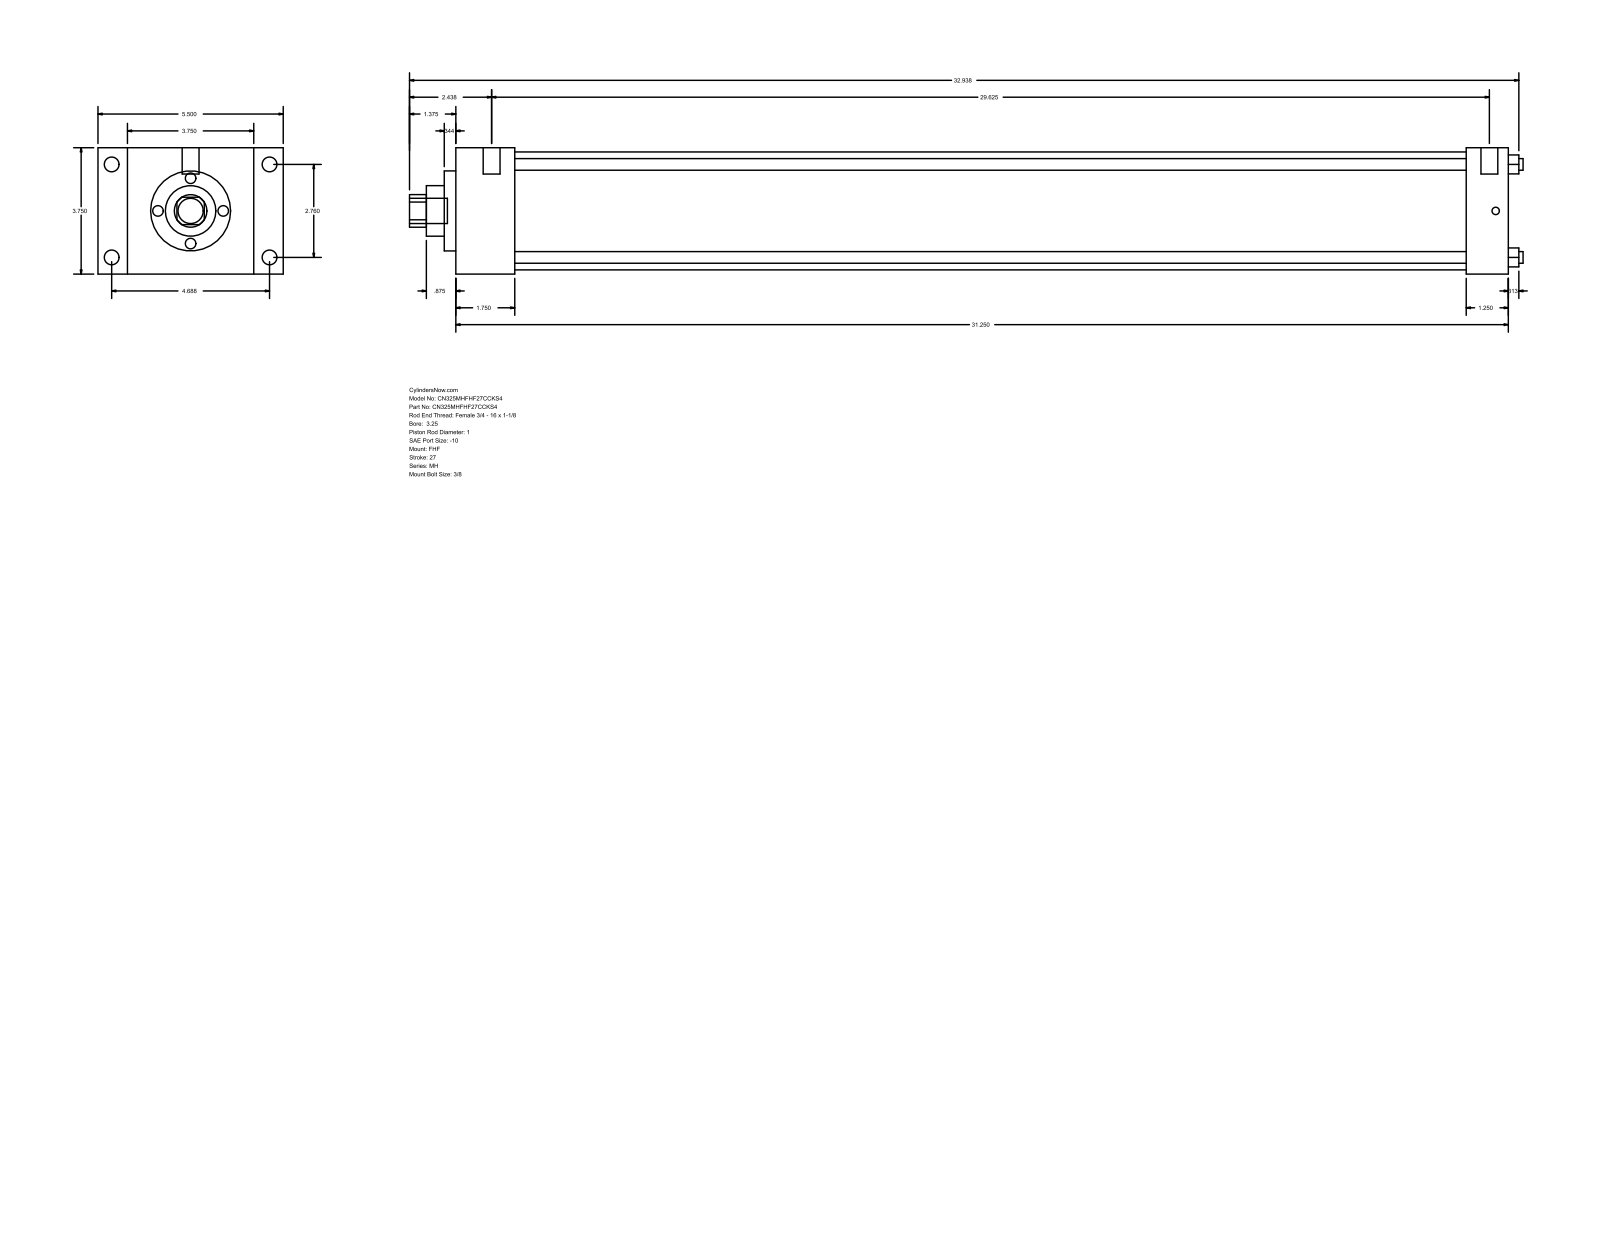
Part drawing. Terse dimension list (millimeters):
name: MH_FHF__0325_1
written by: GSSL Pune (CONFIG_CONTROL_DESIGN)
unit: mm
bodies: 0 solids, 90 faces (61 planar, 29 cylindrical, 0 other)
size: 839.79 × 139.7 × 95.25
holes: 4× ⌀8.76, 1× ⌀25.4, 1× ⌀38.1, 1× ⌀60.33, 1× ⌀88.9
bosses: 4× ⌀11.13, 4× ⌀5.56, 2× ⌀12.7, 1× ⌀19.05
rounds: 1× R12.29
face distances: 95.24, 793.75, 44.46, 749.29, 22.23, 117.47, 139.7, 762, 717.54, 31.75
hole spacings: 49.57, 70.1, 99.14
